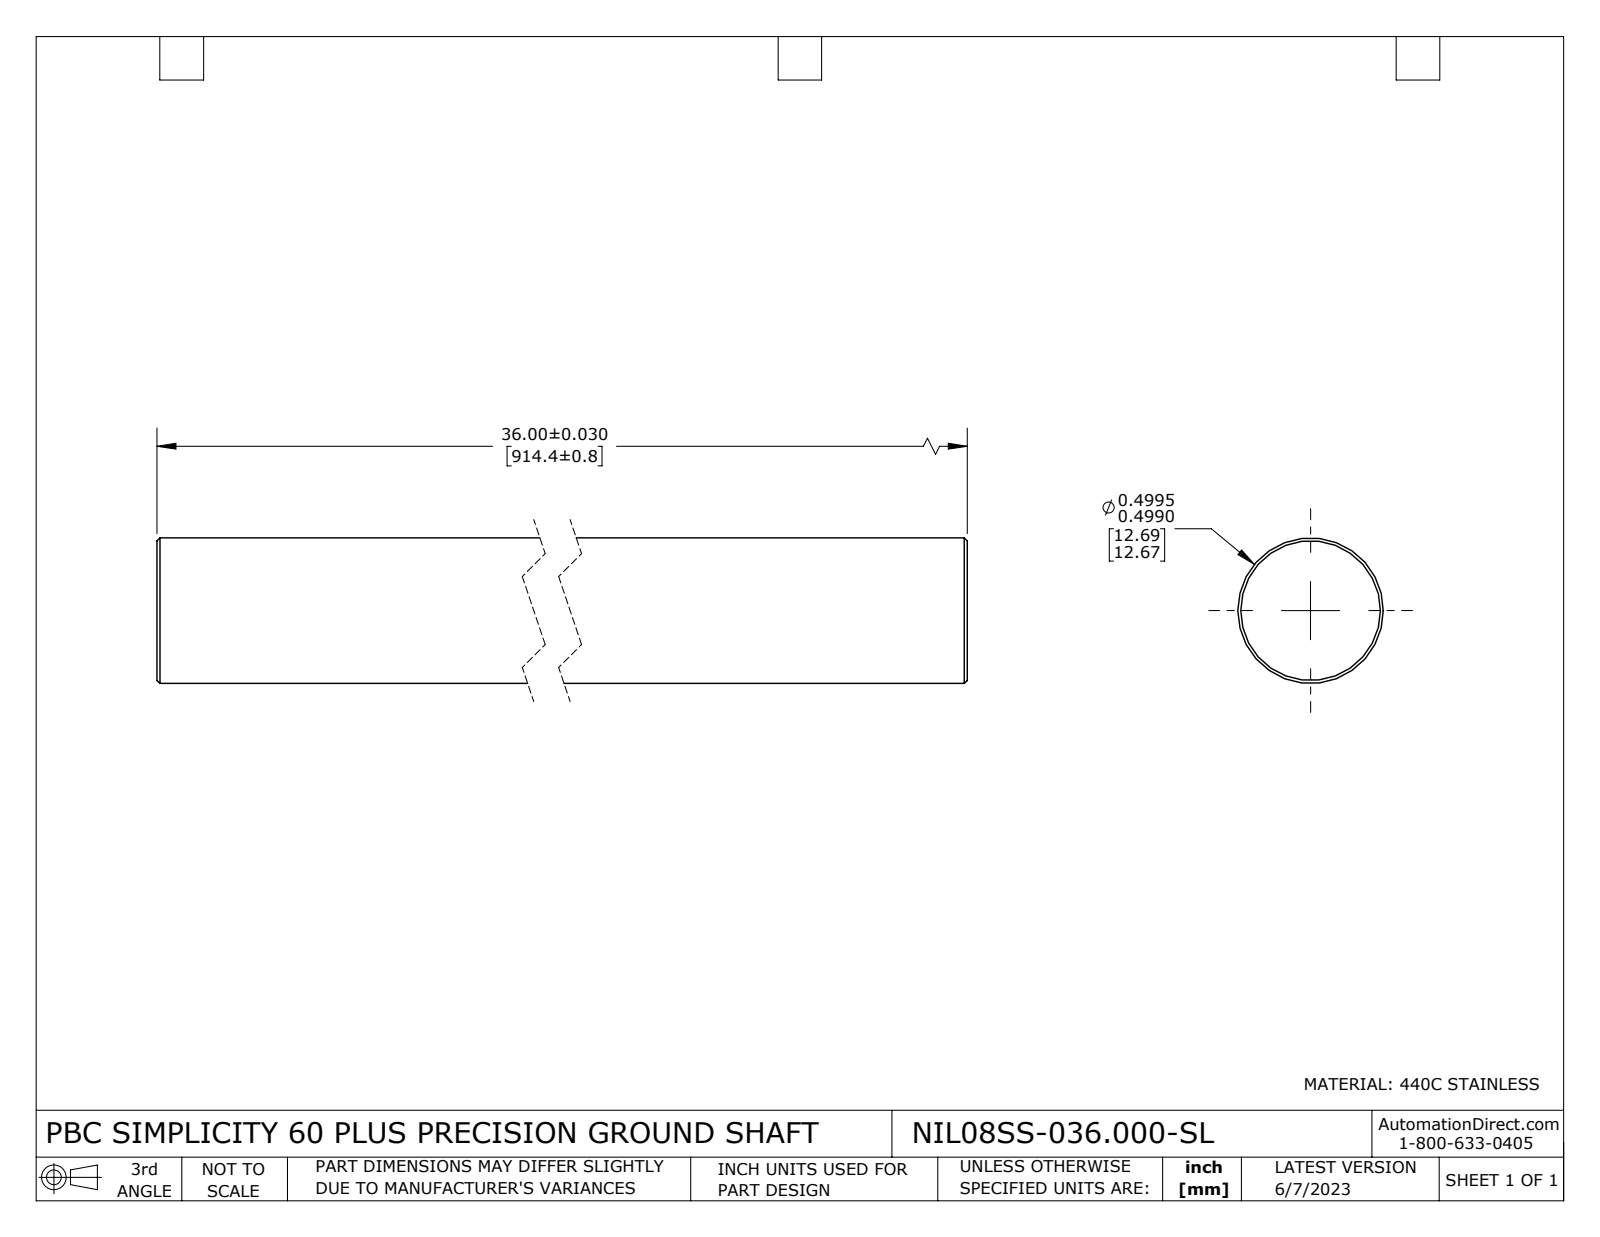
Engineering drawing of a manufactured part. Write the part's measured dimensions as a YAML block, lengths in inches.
part_name: "NIL08SS-036.000-SL"
step_written_by: "SolidWorks 2021 (CONFIG_CONTROL_DESIGN)"
units: inches
bodies: {solids: 1, faces: 8, planar: 2, cylindrical: 2, other: 4}
overall_size: [36, 0.5, 0.5]
volume: 7.068
surface_area: 56.92
round_bosses_or_shafts:
  - {diameter: 0.5, count: 1}
face_to_face_distances: [36]
